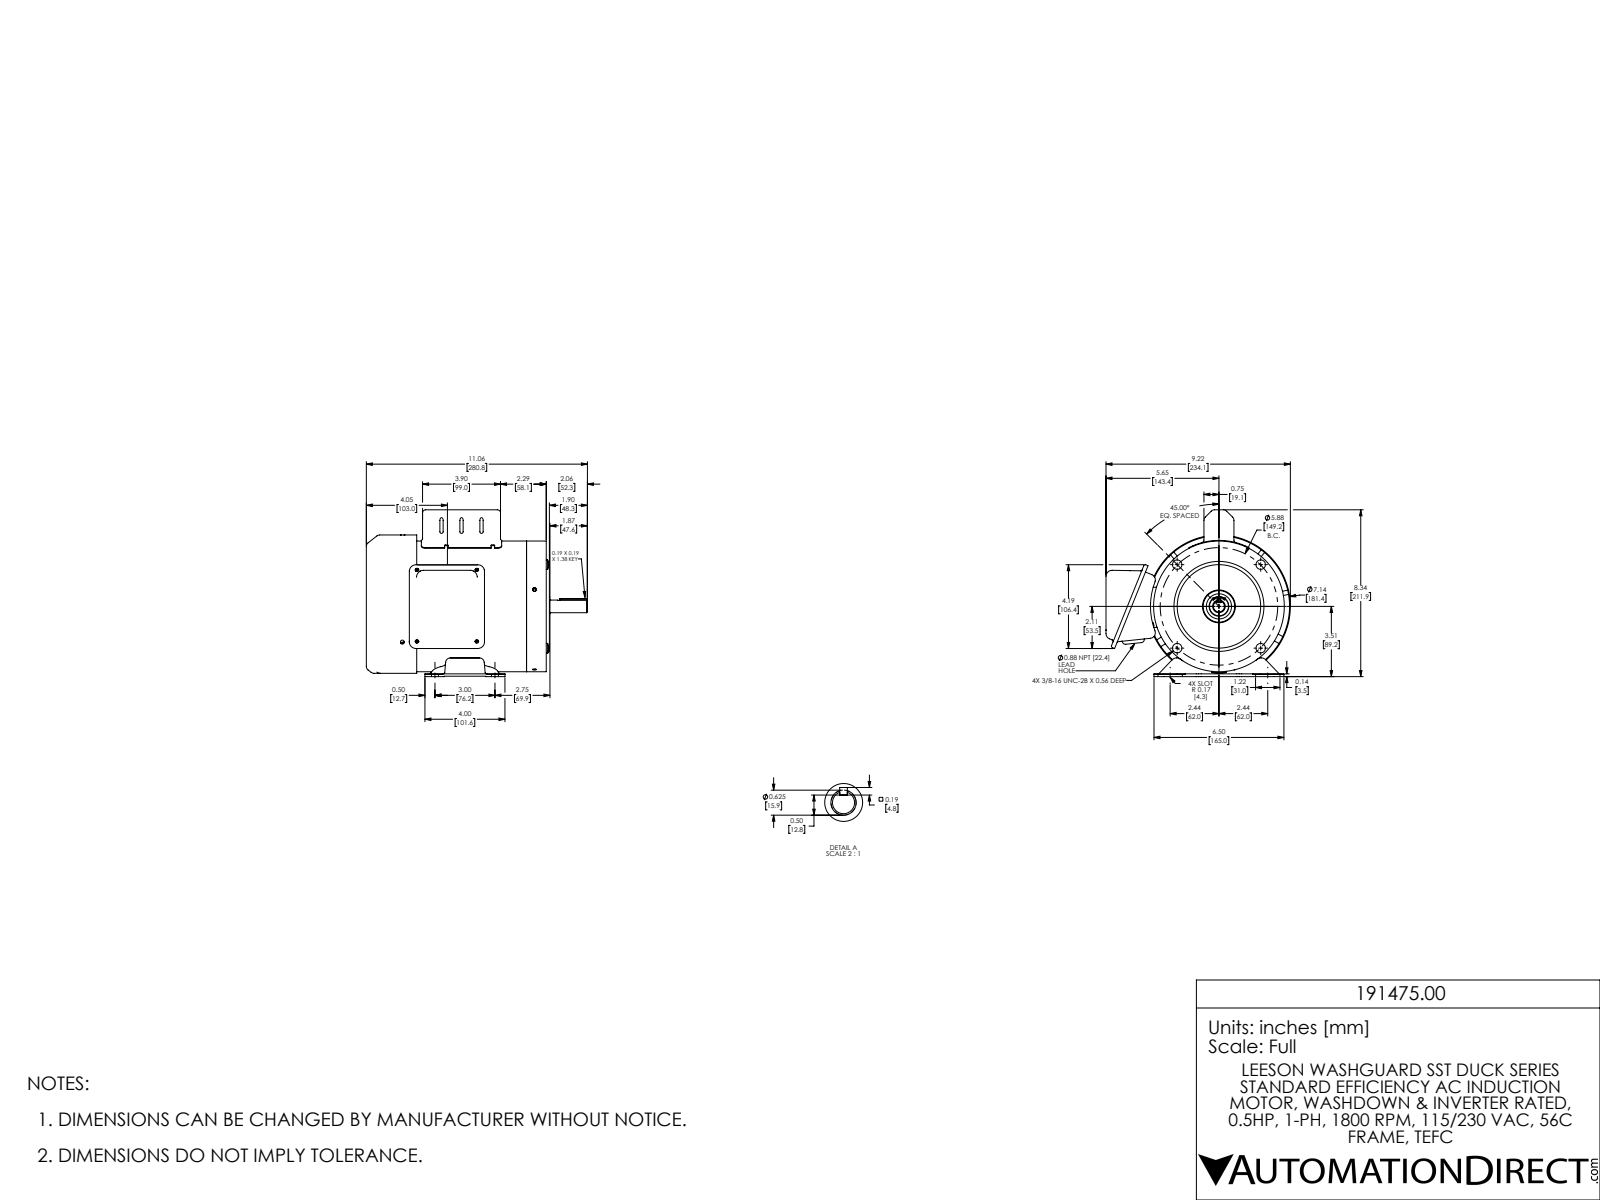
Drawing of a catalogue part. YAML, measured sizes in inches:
part_name: "191475.00"
step_written_by: "SolidWorks 2017 (AUTOMOTIVE_DESIGN)"
units: inches
bodies: {solids: 22, faces: 1819, planar: 376, cylindrical: 829, other: 614}
overall_size: [11.055, 9.218, 8.341]
volume: 59.41
surface_area: 1048
round_holes:
  - {diameter: 0.197, count: 15}
  - {diameter: 0.13, count: 14}
  - {diameter: 0.138, count: 9}
  - {diameter: 0.165, count: 8}
  - {diameter: 0.268, count: 8}
  - {diameter: 0.177, count: 6}
  - {diameter: 0.315, count: 6}
  - {diameter: 0.228, count: 4}
  - {diameter: 0.157, count: 2}
  - {diameter: 1.378, count: 2}
  - {diameter: 0.189, count: 1}
  - {diameter: 0.63, count: 1}
round_bosses_or_shafts:
  - {diameter: 0.472, count: 4}
  - {diameter: 0.319, count: 4}
  - {diameter: 7.142, count: 1}
  - {diameter: 7.063, count: 1}
  - {diameter: 6.535, count: 1}
  - {diameter: 5.039, count: 1}
  - {diameter: 4.5, count: 1}
  - {diameter: 2.362, count: 1}
partial_cylinders:
  - {radius: 0.094, count: 81}
  - {radius: 0.079, count: 44}
  - {radius: 0.236, count: 31}
  - {radius: 0.157, count: 26}
  - {radius: 0.039, count: 16}
  - {radius: 0.02, count: 14}
  - {radius: 0.276, count: 13}
  - {radius: 0.098, count: 12}
face_to_face_distances: [0.039, 0.118, 0.197, 0.236, 7.283, 8.76, 1.161, 0.984, 7.598, 7.972]
hole_center_spacings: [3.858, 0.236, 4.176, 2.992, 4.883, 1.496, 2.953, 0.017]
